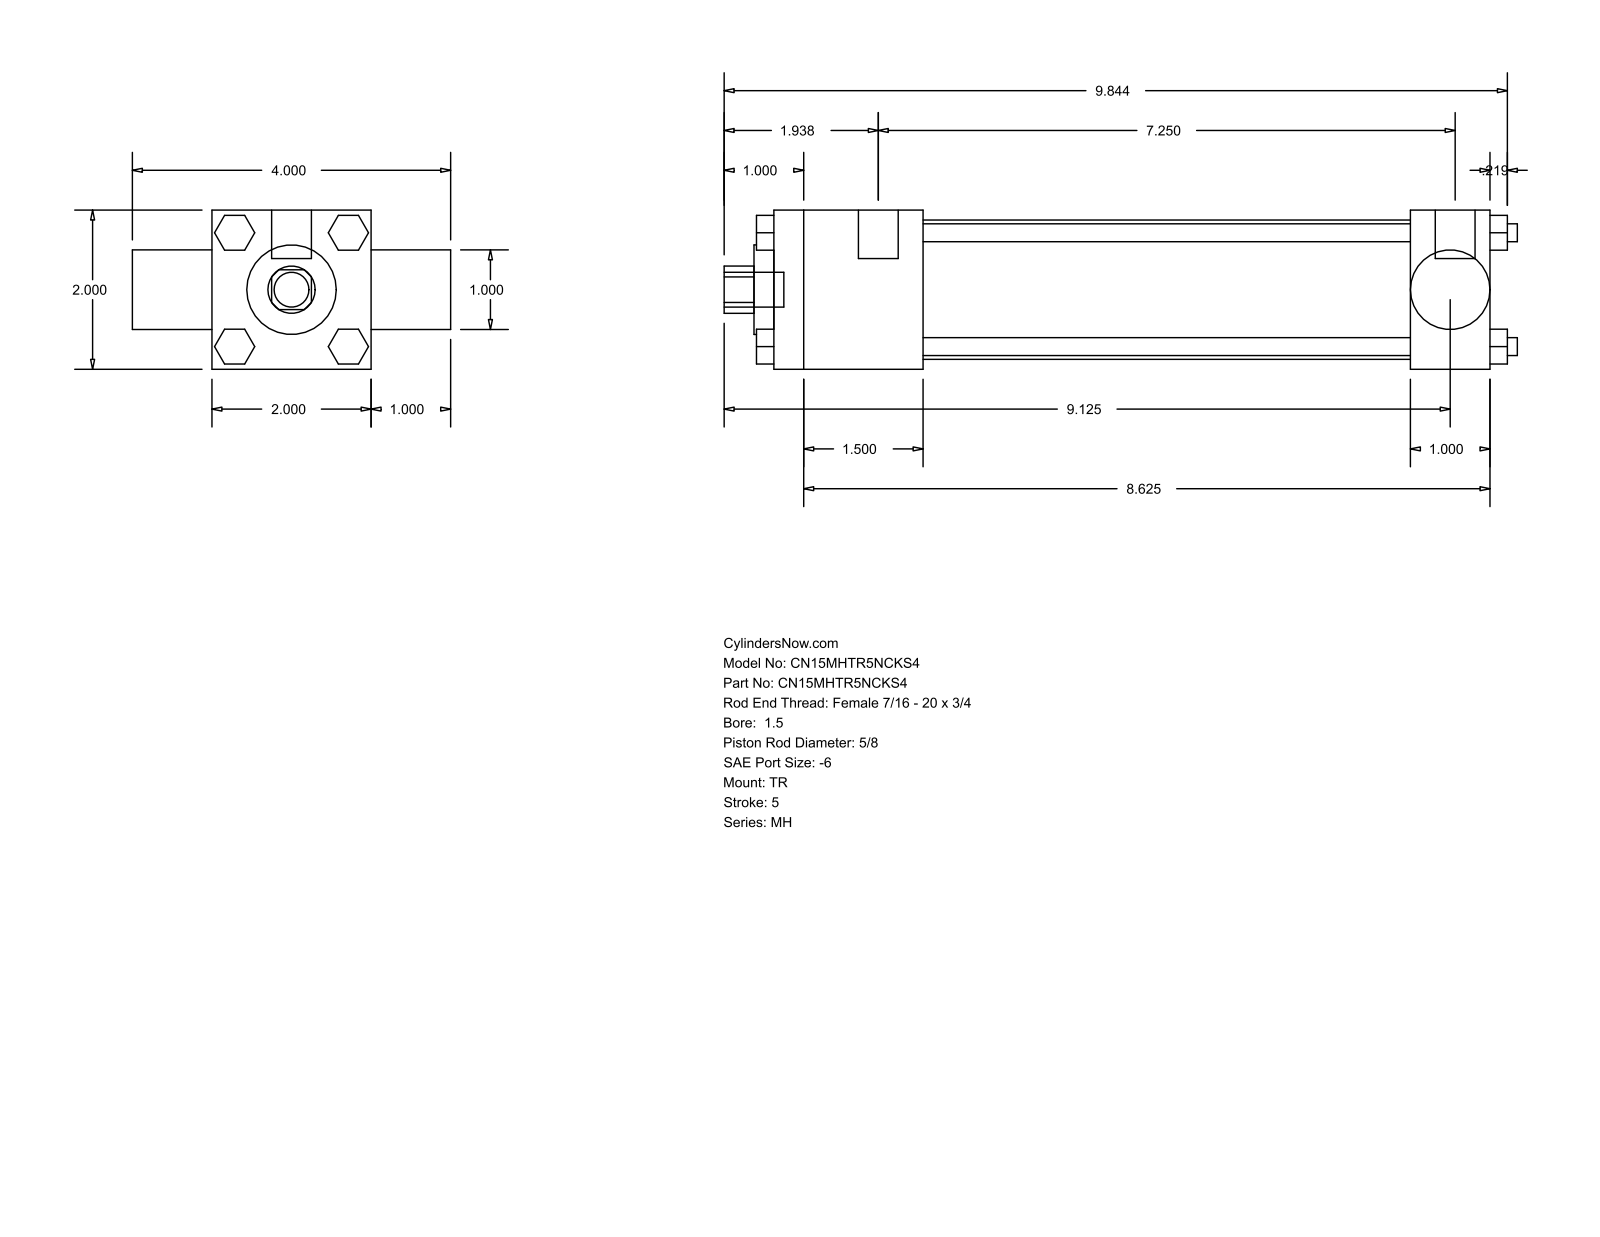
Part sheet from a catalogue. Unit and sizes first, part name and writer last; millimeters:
Units: millimetres
Overall size (bounding box): 253.21 × 101.6 × 50.8
Round holes (diameter × count): ⌀15.88 ×1, ⌀25.35 ×1, ⌀28.57 ×1, ⌀44.45 ×1
Round bosses / shafts (diameter × count): ⌀5.71 ×4, ⌀5.56 ×3, ⌀12.7 ×2, ⌀11.11 ×1
Partial cylindrical surfaces — rounded edges, fillets, slot ends (radius × count): R7.54 ×1
Main face-to-face distances: 50.8, 25.4, 228.59, 76.2, 47.62, 180.97, 203.19, 155.57, 5.56, 234.15
Bodies: 0 solids, 120 faces (92 planar, 28 cylindrical, 0 other)
Part name (STEP PRODUCT): MH_TR__0150_0.625
STEP written by: GSSL Pune (CONFIG_CONTROL_DESIGN)
